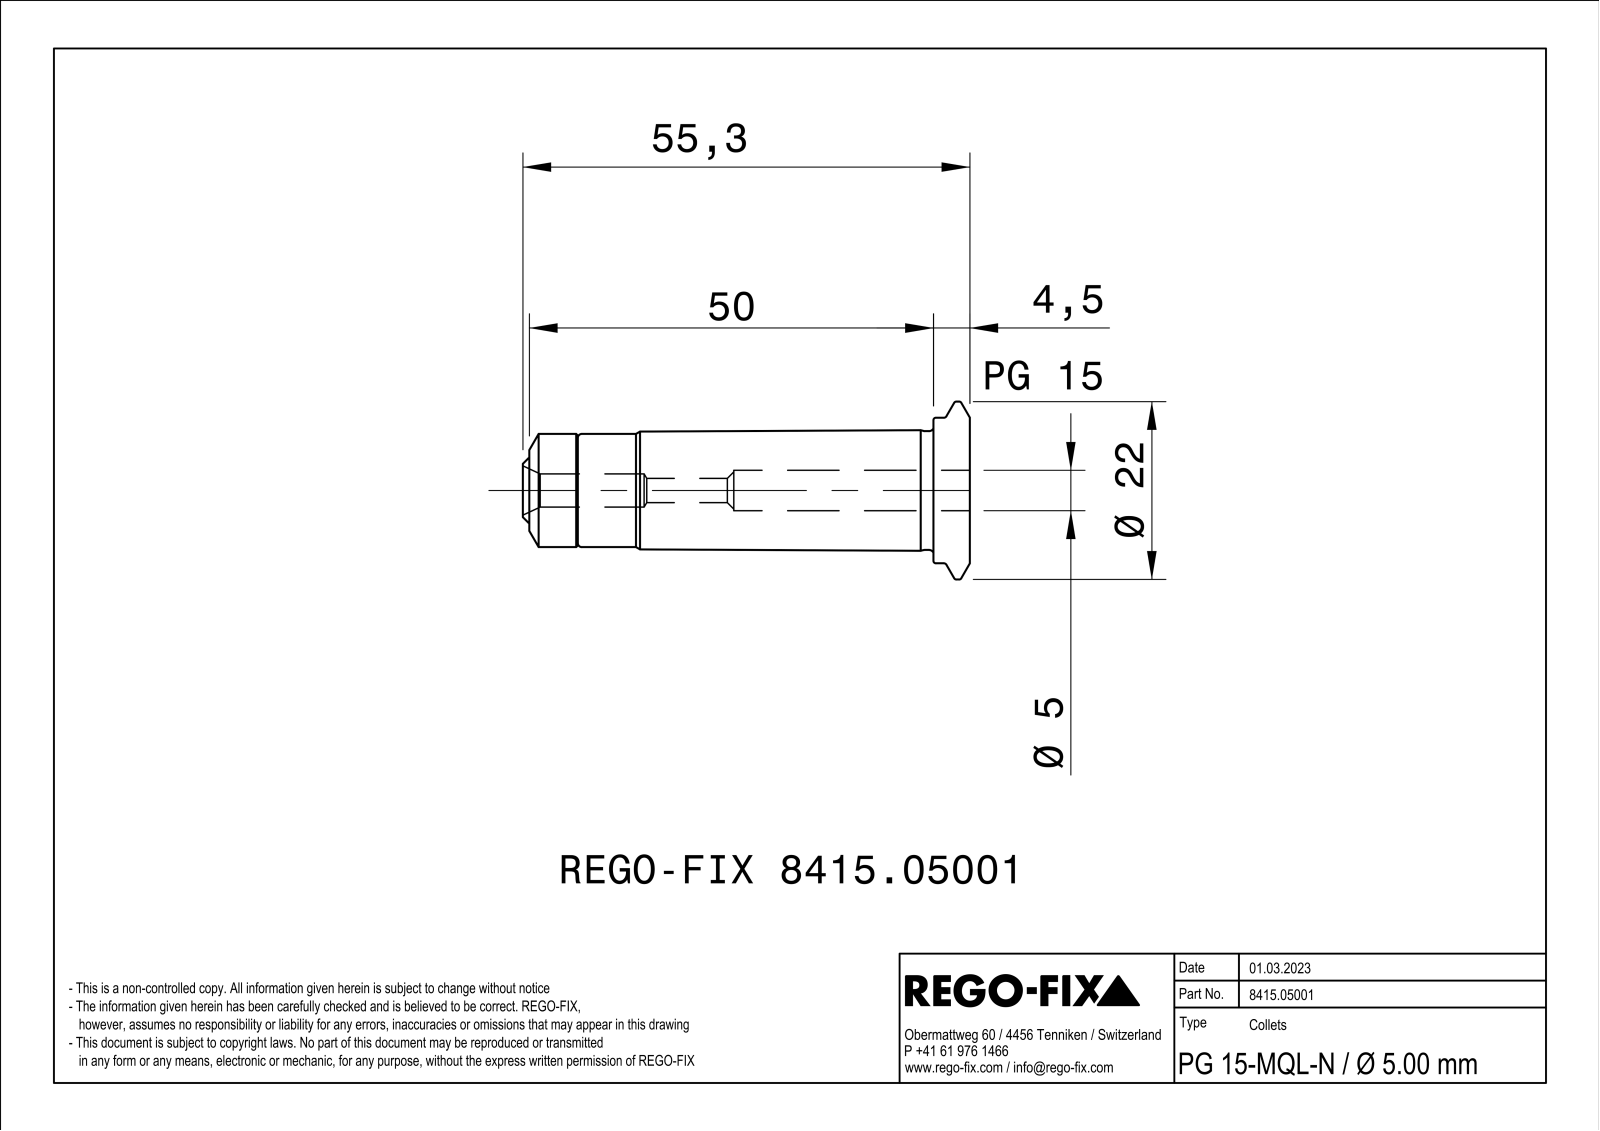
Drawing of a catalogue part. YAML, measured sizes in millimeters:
part_name: "NOCUT"
step_written_by: "SIEMENS PLM Software Solid Edge ST10 (AUTOMOTIVE_DESIGN)"
units: millimeters
bodies: {solids: 1, faces: 81, planar: 16, cylindrical: 19, other: 46}
overall_size: [55.3, 22, 21.99]
volume: 2461
surface_area: 6096
round_holes:
  - {diameter: 3, count: 1}
  - {diameter: 4.1, count: 1}
  - {diameter: 5, count: 1}
  - {diameter: 8.5, count: 1}
  - {diameter: 10.92, count: 1}
  - {diameter: 12.2, count: 1}
round_bosses_or_shafts:
  - {diameter: 22, count: 1}
  - {diameter: 18, count: 1}
  - {diameter: 14.7, count: 1}
  - {diameter: 14, count: 1}
  - {diameter: 11.55, count: 1}
  - {diameter: 8, count: 1}
face_to_face_distances: [1, 48.5, 6, 54.5, 4.5, 44, 50, 42.5, 38, 12]
